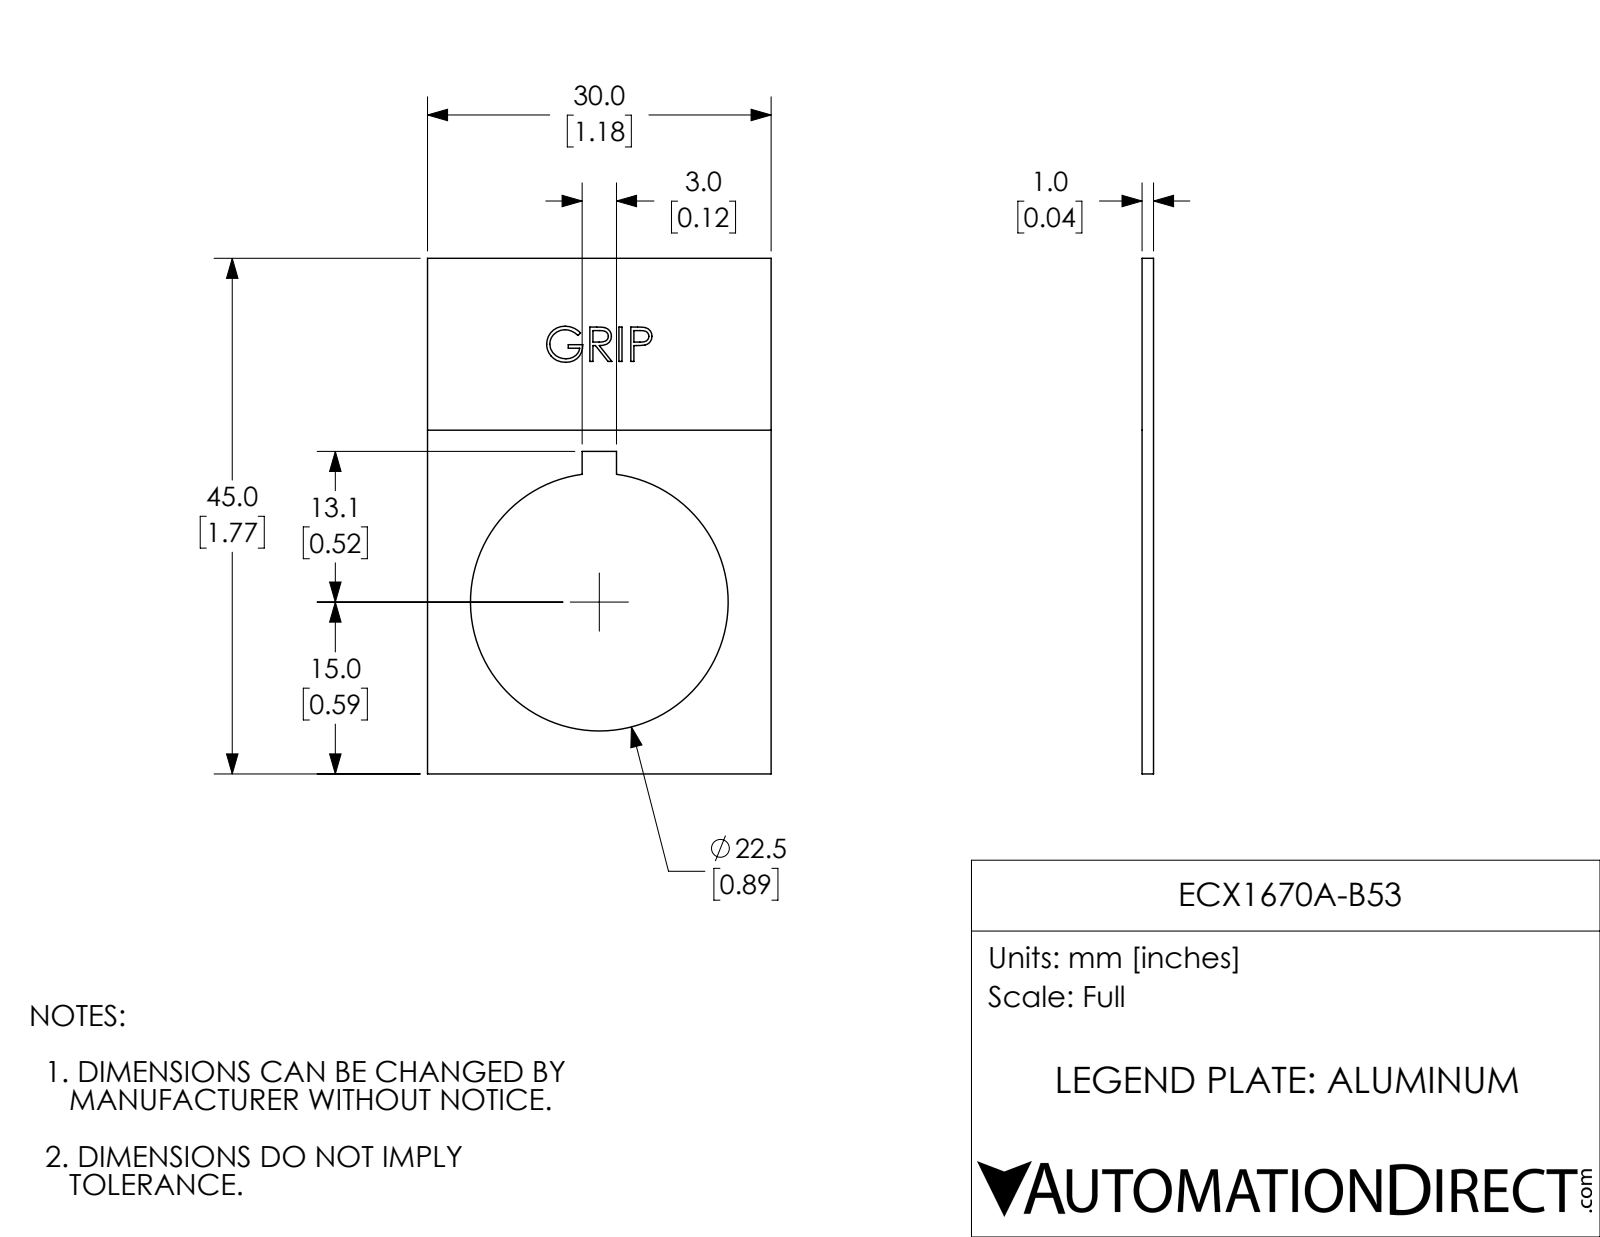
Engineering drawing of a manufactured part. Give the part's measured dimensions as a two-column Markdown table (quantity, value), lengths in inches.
| quantity | value |
| --- | --- |
| part name | ECX1670A-B53 |
| STEP written by | SolidWorks 2017 (AUTOMOTIVE_DESIGN) |
| units | inches |
| bodies | 1 solid, 66 faces (43 planar, 3 cylindrical, 20 other) |
| overall size | 1.772 × 1.181 × 0.039 |
| volume | 0.058 in³ |
| surface area | 3.285 in² |
| round holes (diameter × count) | 0.886 × 1 |
| main face-to-face distances | 0.039, 1.181, 1.772, 0.038, 0.531, 0.65, 1.108, 0.663, 0.118, 0.041 |
